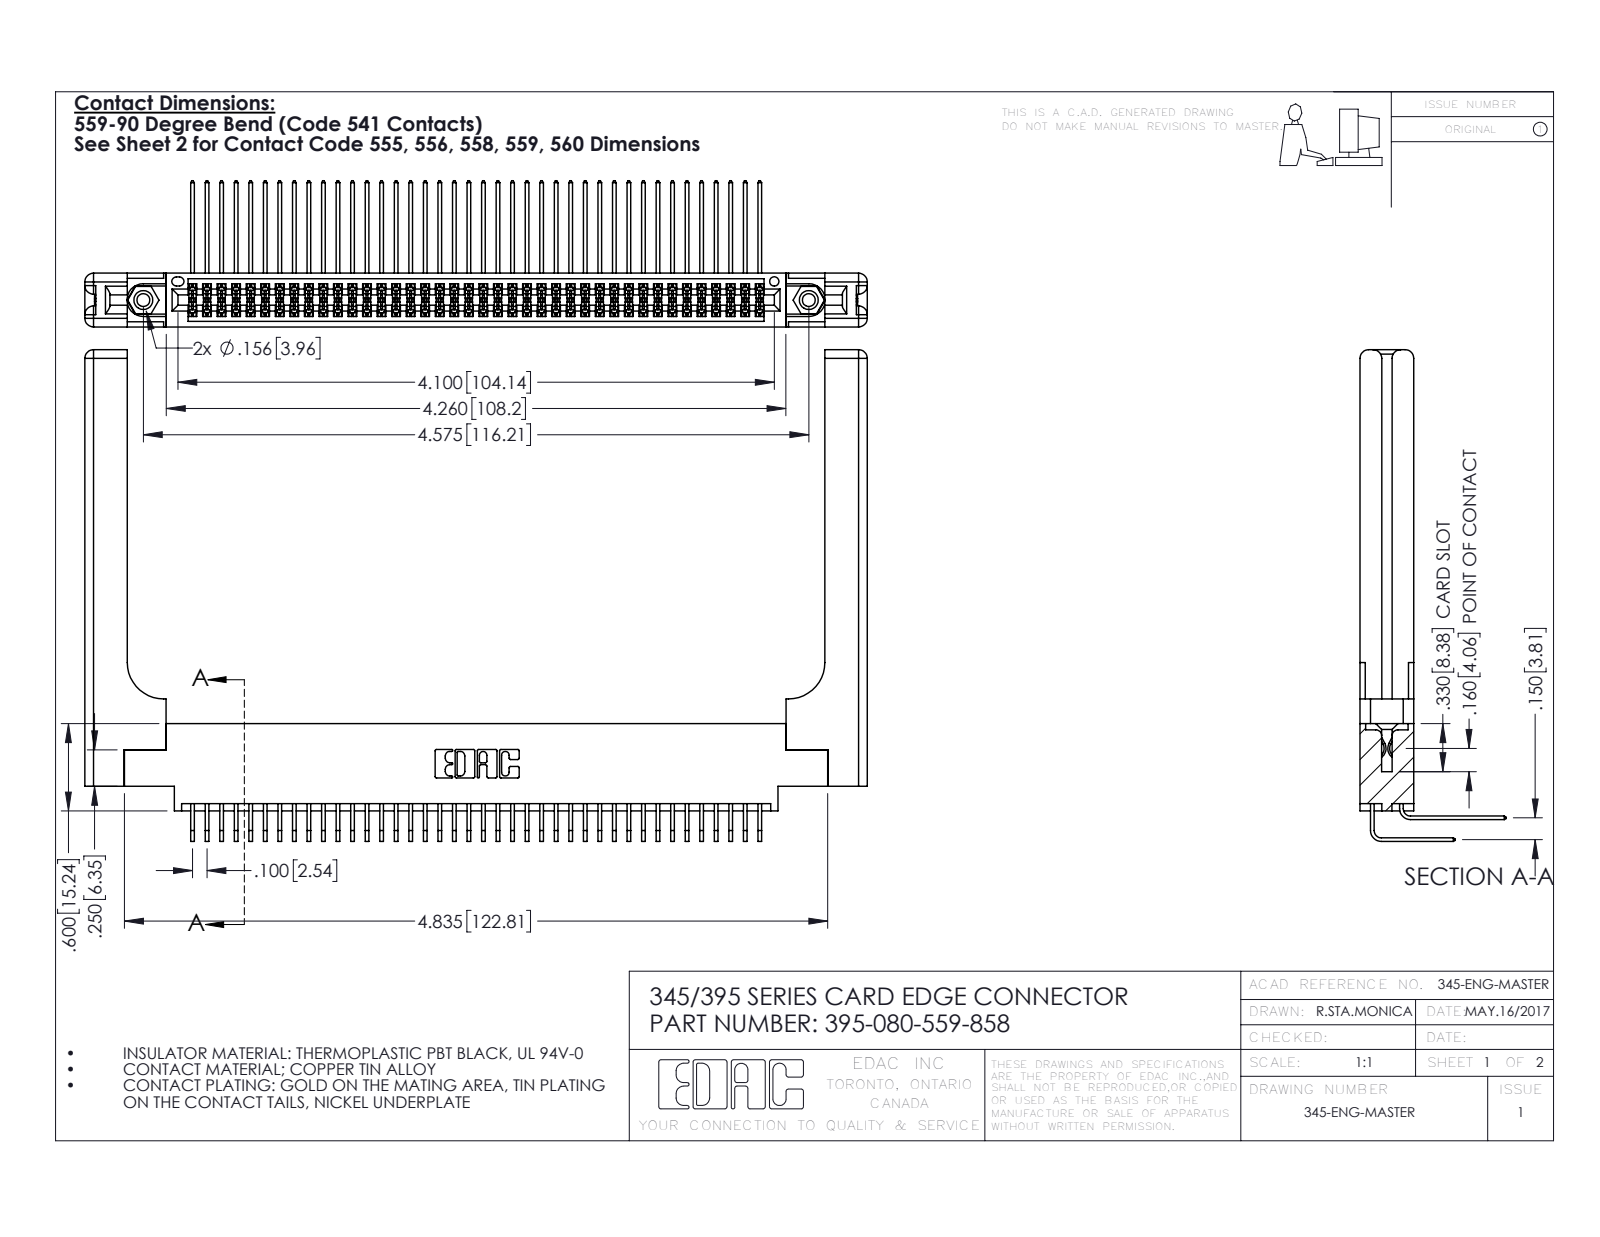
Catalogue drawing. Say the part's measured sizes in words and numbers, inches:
The part is named "395-080-559-858; 345-292-001_559 Tail - 2; 345-250-001_345-250-001-102; 345 Part_0.170 Offset - 0.156 Dia-TH (+2 more)". Its 3-D file was written by "SolidWorks 2016 (CONFIG_CONTROL_DESIGN)". It is 85 solids with 4546 faces: 3032 planar, 1454 cylindrical and 60 other. Overall it measures 5.379 by 3.379 by 1.005 inches. Its volume is 1.347 cubic inches and its surface area 42.53 square inches. Round holes: 2 of diameter 0.089, 2 of diameter 0.125, 2 of diameter 0.156, 1 of diameter 0.064. Round bosses or shafts: 2 of diameter 0.155. Partial cylindrical surfaces (rounded edges, fillets, slot ends): 120 of radius 0.006, 22 of radius 0.01, 16 of radius 0.06, 6 of radius 0.007, 6 of radius 0.031, 3 of radius 0.026, 2 of radius 0.014, 2 of radius 0.019. The main face-to-face distances are 0.072, 0.37, 0.298, 0.098, 0.272, 0.025, 0.2, 0.225, 0.15, 0.175. The hole center spacings are 0.27, 4.339, 4.575.
